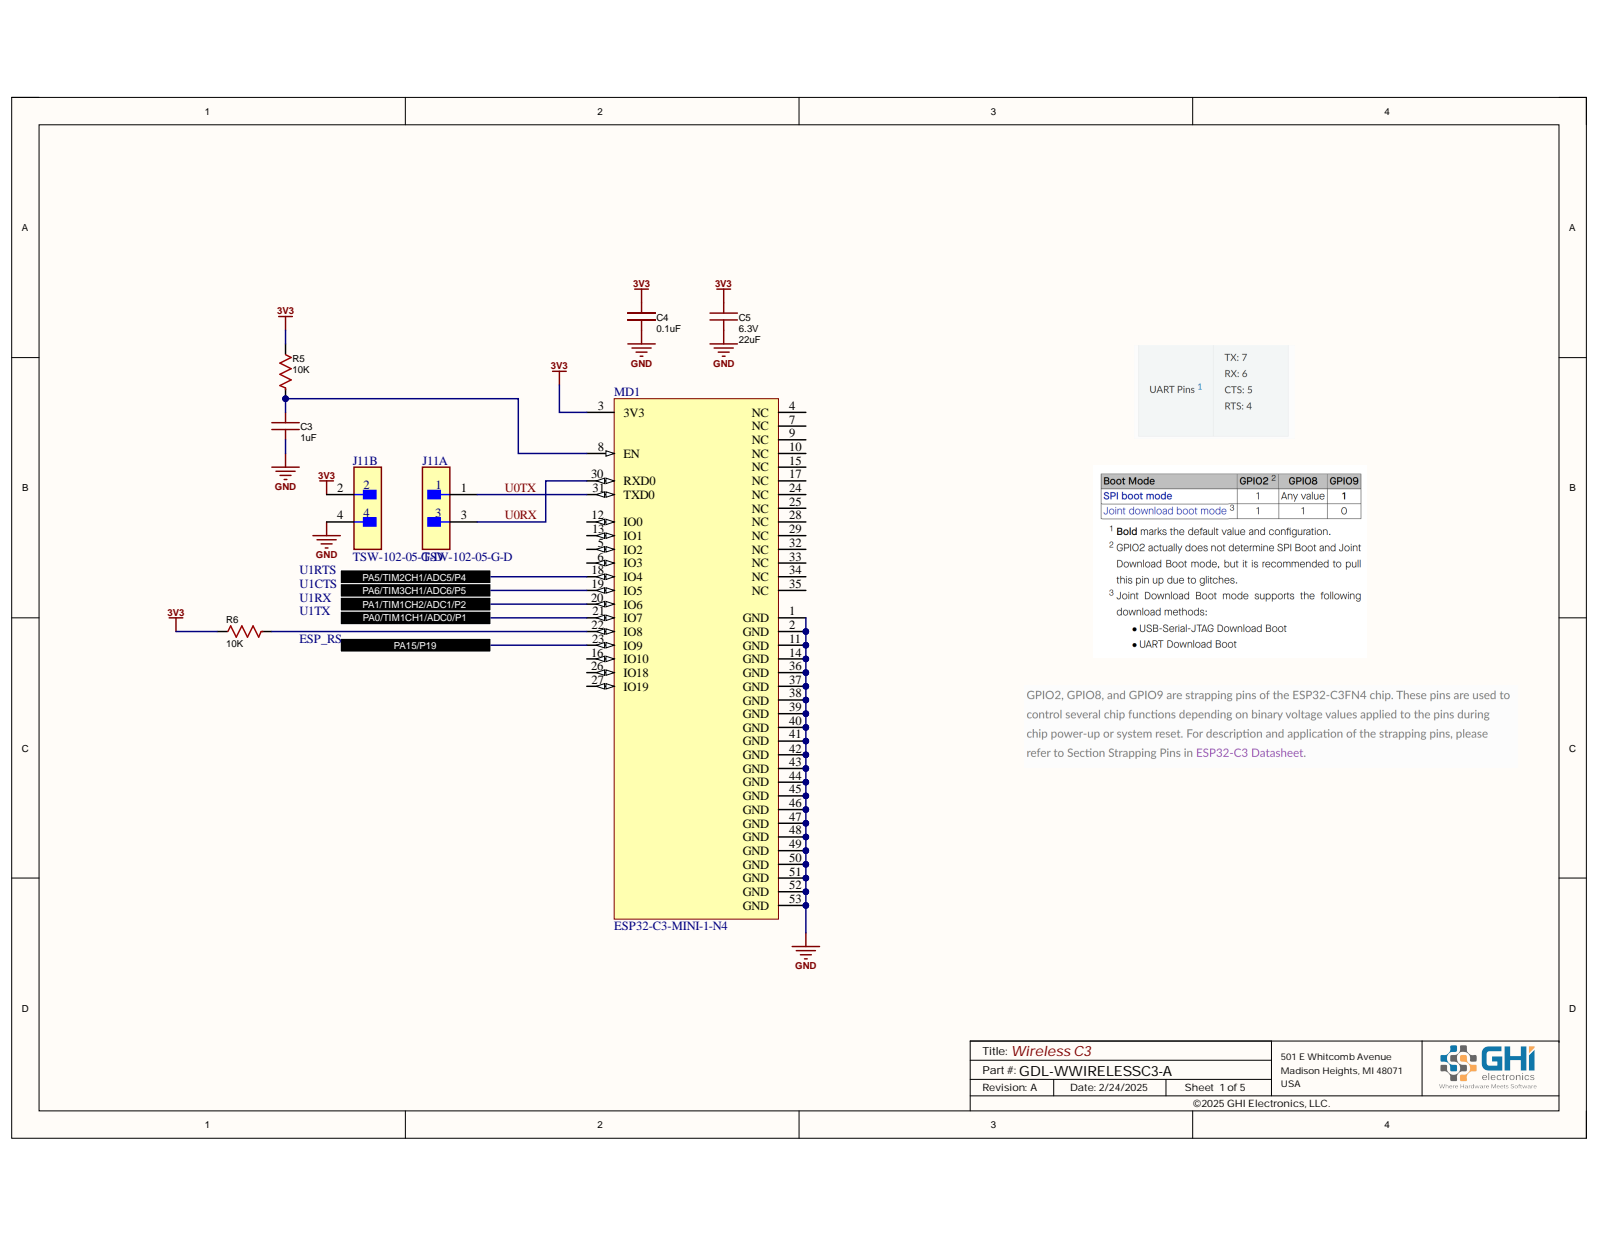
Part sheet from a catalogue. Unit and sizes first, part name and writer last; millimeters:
Units: millimetres
Overall size (bounding box): 32 × 27 × 8.84
Round holes (diameter × count): ⌀0.25 ×10, ⌀1.02 ×4, ⌀3 ×4, ⌀1.02 ×2
Round bosses / shafts (diameter × count): ⌀0.61 ×1, ⌀0.2 ×1
Partial cylindrical surfaces — rounded edges, fillets, slot ends (radius × count): R0.12 ×35, R0.15 ×26, R0.1 ×4, R0.3 ×4, R3.5 ×4, R0.17 ×2, R0.18 ×2, R0.18 ×2
Main face-to-face distances: 1, 0.8, 2.55, 2.35, 0.6, 1.75, 0.7, 2.75, 1.55, 0.4
Hole centre spacings: 2.1, 3.58, 2.54, 2.9, 4.2, 5.1, 3.59, 6.3
Volume: 533 mm³ · Surface area: 3 577 mm²
Bodies: 202 solids, 3122 faces (2387 planar, 384 cylindrical, 351 other)
Part name (STEP PRODUCT): PCB; Board; J11; Conn_Samtec_TSW-102-05-G-D_eec (+7 more)
STEP written by: Open CASCADE 7.5 (AUTOMOTIVE_DESIGN)
